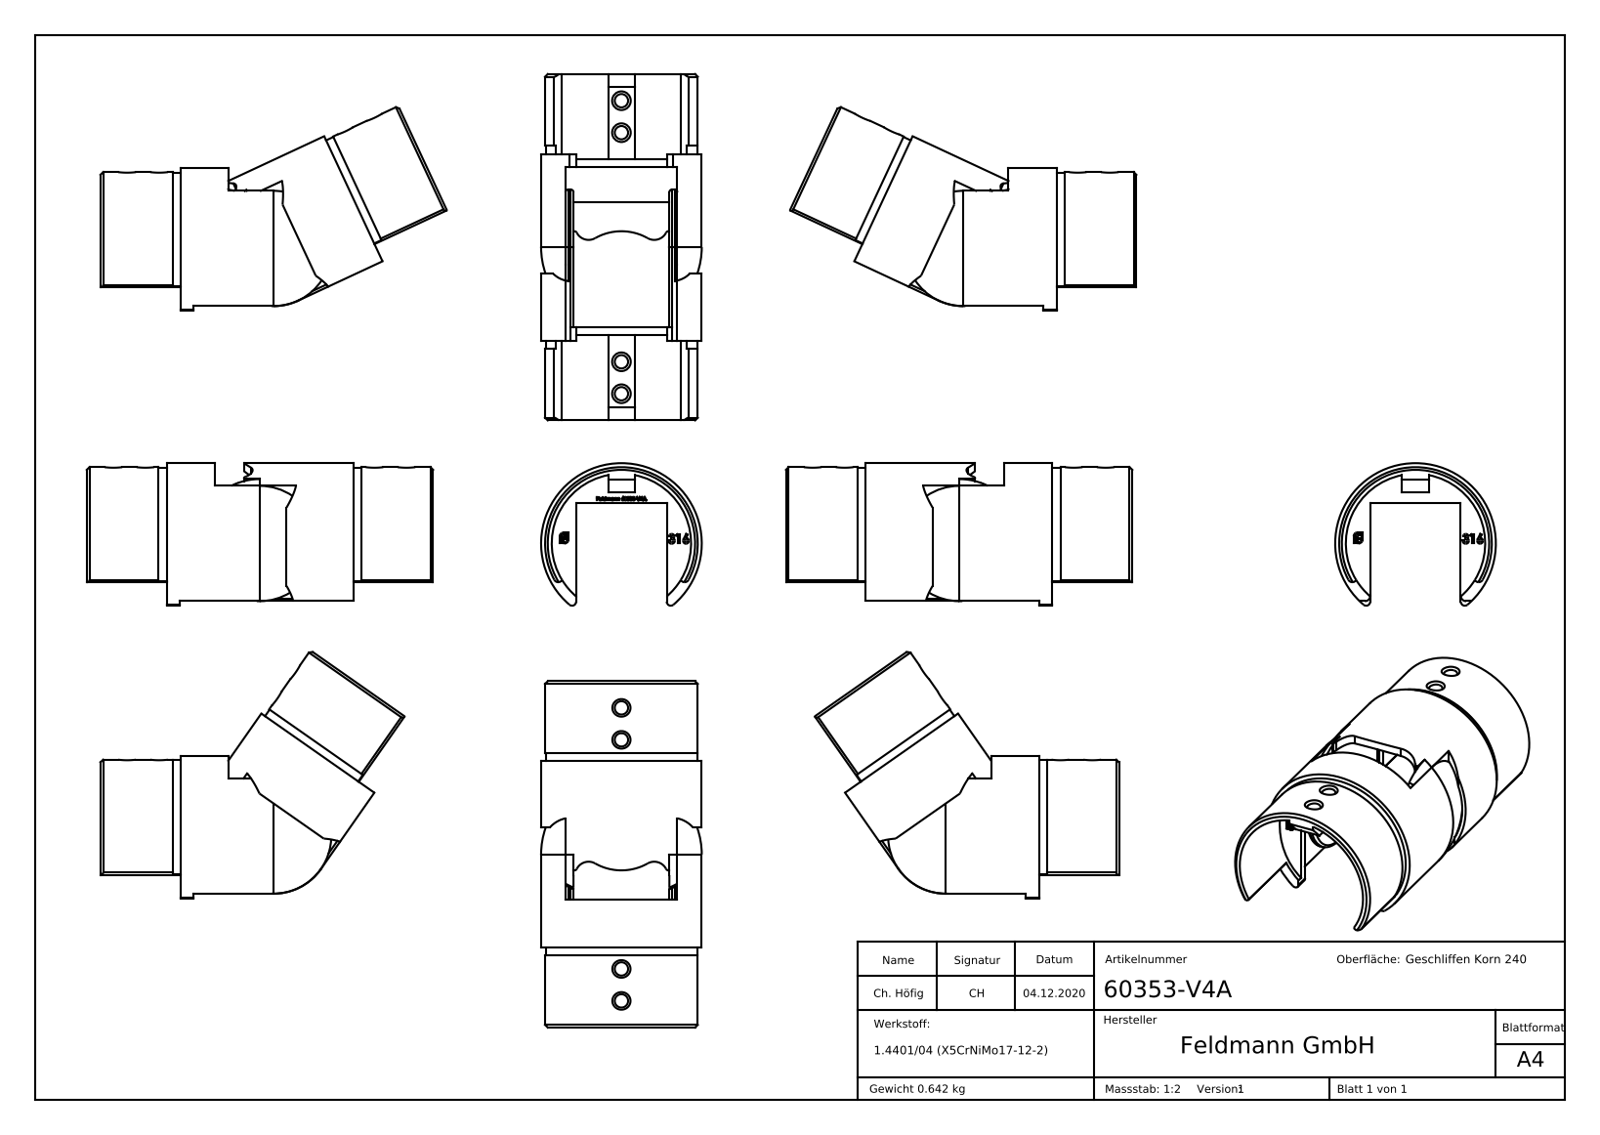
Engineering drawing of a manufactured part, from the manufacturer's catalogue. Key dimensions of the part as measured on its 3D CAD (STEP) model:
Part name (STEP PRODUCT): 60353-V4A Teil2; 60353-V4A Teil2_60312-240 fr 60,3 Teil2; 60353-V4A Teil1; 60353-V4A (+1 more)
STEP written by: SolidWorks 2018 (CONFIG_CONTROL_DESIGN)
Units: millimetres
Bodies: 2 solids, 532 faces (247 planar, 66 cylindrical, 219 other)
Overall size (bounding box): 130 × 60.3 × 53.5
Volume: 80 194 mm³ · Surface area: 45 431 mm²
Round holes (diameter × count): ⌀5 ×4, ⌀10 ×1
Partial cylindrical surfaces — rounded edges, fillets, slot ends (radius × count): R1 ×6, R1.52 ×2, R1.7 ×2, R2 ×2, R5 ×2, R10 ×2, R11 ×2, R20 ×1
Main face-to-face distances: 3, 39, 42, 36, 63, 23, 16, 13, 35, 26
Hole centre spacings: 12, 98, 86, 110
